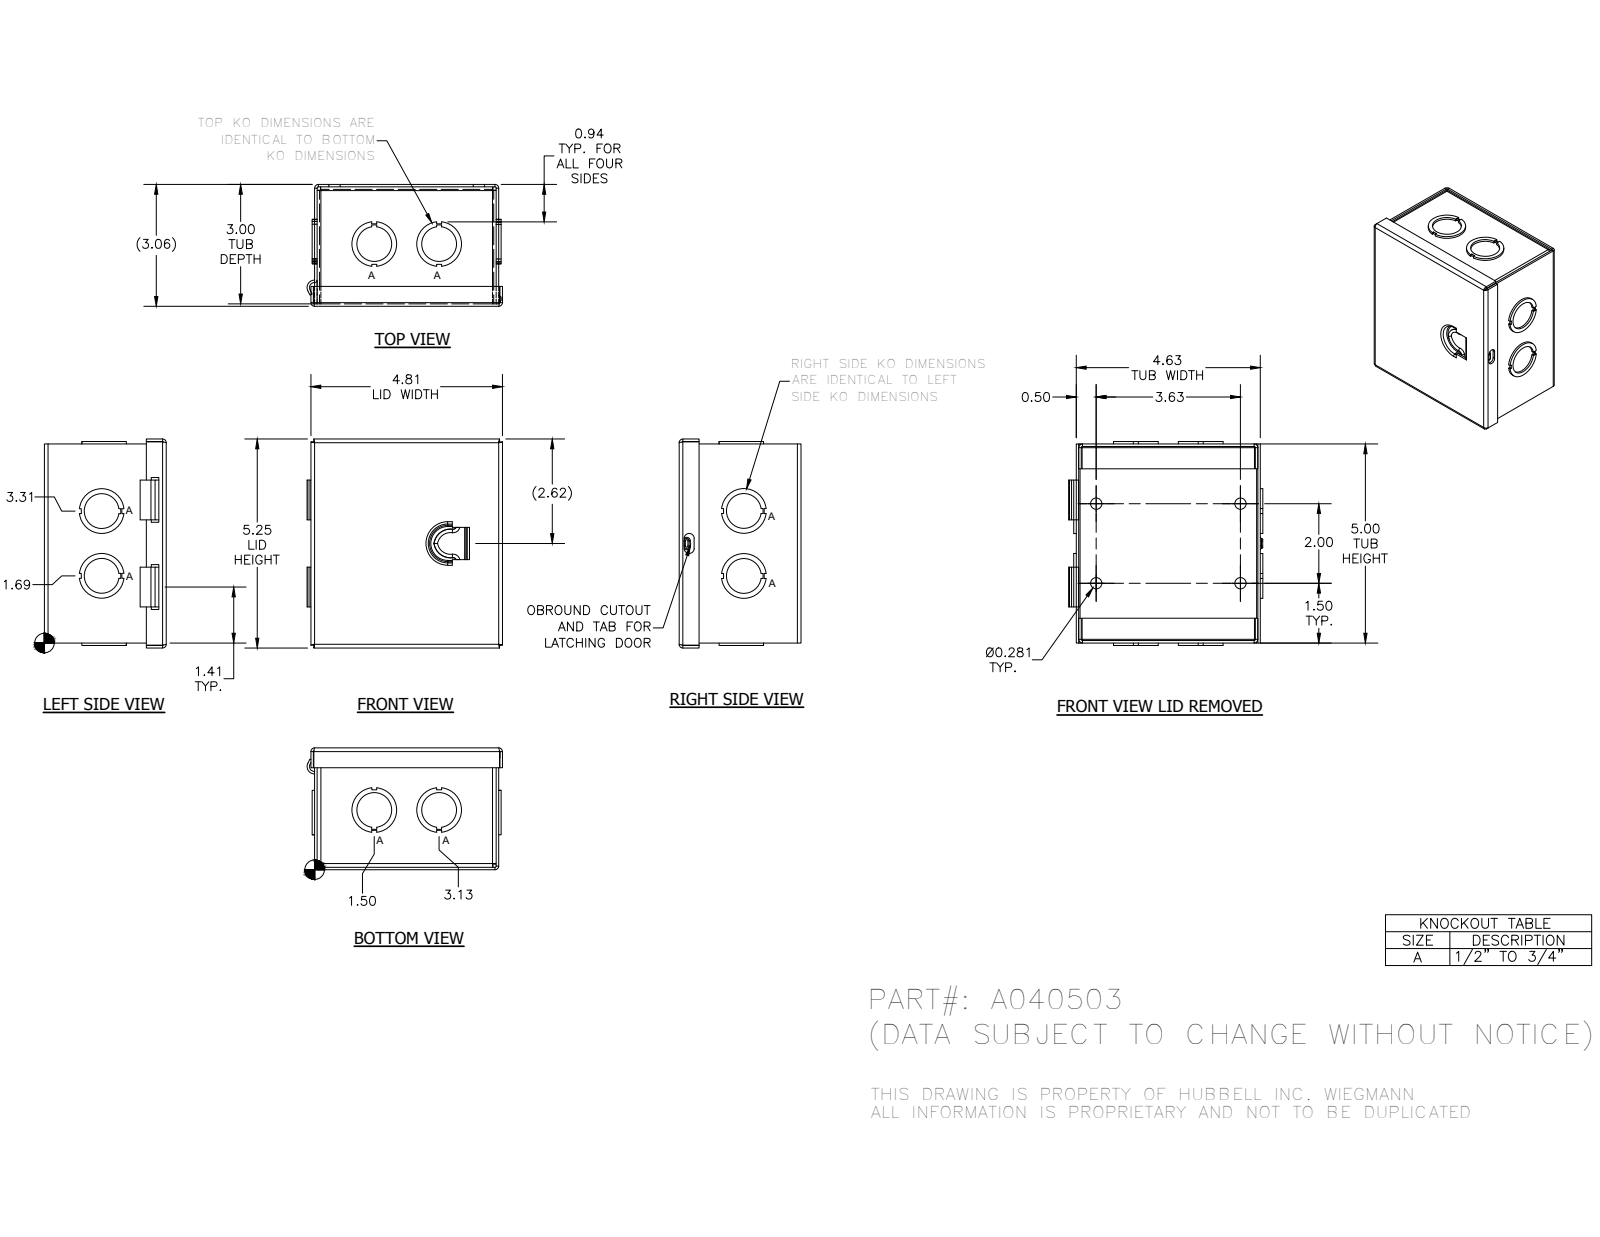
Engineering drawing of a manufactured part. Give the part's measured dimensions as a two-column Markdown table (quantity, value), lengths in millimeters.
| quantity | value |
| --- | --- |
| part name | A040503BLR; A0403TB; A0405LFA; 35010 (+1 more) |
| STEP written by | Autodesk Inventor 2014 (AUTOMOTIVE_DESIGN) |
| units | millimeters |
| bodies | 18 solids, 445 faces (305 planar, 105 cylindrical, 35 other) |
| overall size | 134.91 × 126.26 × 77.79 |
| round holes (diameter × count) | 22.22 × 6, 28.57 × 6, 7.14 × 4 |
| partial cylindrical surfaces (radius × count) | 0.79 × 18, 2.38 × 8, 3.17 × 7, 0.79 × 4, 2.37 × 4, 1.59 × 3, 1.54 × 1, 3.2 × 1 |
| main face-to-face distances | 1.59, 1.58, 115.89, 74.62, 76.2, 125.41, 114.3, 76.21, 77.79, 127 |
| hole center spacings | 41.33, 41.4, 50.8, 92.08, 105.16, 41.26 |
